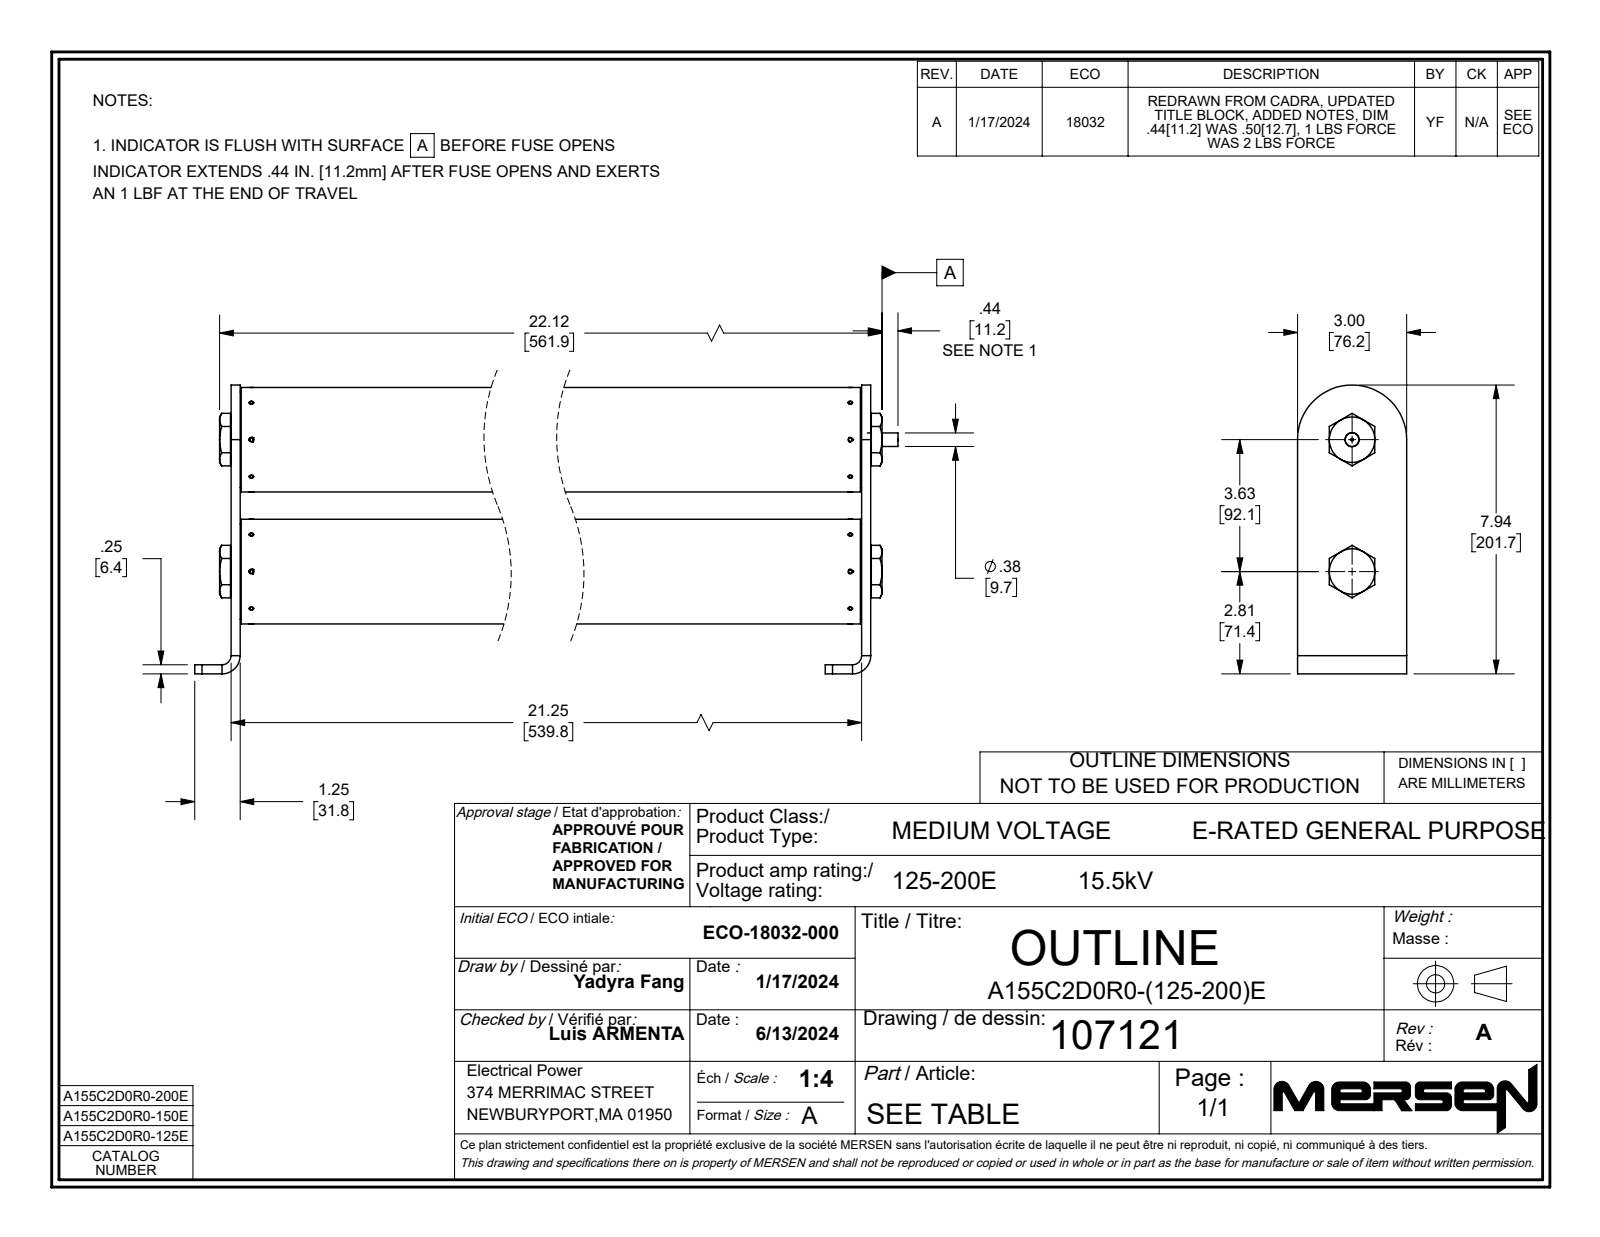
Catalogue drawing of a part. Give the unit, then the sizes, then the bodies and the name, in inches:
Units: inches
Overall size (bounding box): 22.812 × 7.94 × 3
Round holes (diameter × count): ⌀0.125 ×24, ⌀0.906 ×2, ⌀2.37 ×2, ⌀2.5 ×2, ⌀0.02 ×1, ⌀0.063 ×1, ⌀0.146 ×1, ⌀0.189 ×1, ⌀0.391 ×1, ⌀0.465 ×1, ⌀0.512 ×1, ⌀2.625 ×1
Round bosses / shafts (diameter × count): ⌀0.125 ×24, ⌀0.25 ×4, ⌀2.875 ×2, ⌀1.25 ×2, ⌀0.875 ×2, ⌀0.782 ×2, ⌀2.625 ×1, ⌀2.625 ×1
Partial cylindrical surfaces — rounded edges, fillets, slot ends (radius × count): R4 ×111, R0.01 ×36, R0.2 ×4, R0.828 ×3, R0.984 ×3, R0.25 ×2, R0.5 ×2, R1.5 ×1
Main face-to-face distances: 0.25, 21.25, 21.5, 21, 21.812, 0.562, 0.281, 0.312, 21.562, 0.593
Hole centre spacings: 20.38, 20.541, 2.563, 2.563, 3.625, 3.625, 20.7, 20.7
Volume: 61.41 in³ · Surface area: 891.5 in²
Bodies: 59 solids, 3887 faces (983 planar, 1644 cylindrical, 1260 other)
Part name (STEP PRODUCT): 107121
STEP written by: SolidWorks 2021 (AUTOMOTIVE_DESIGN)
